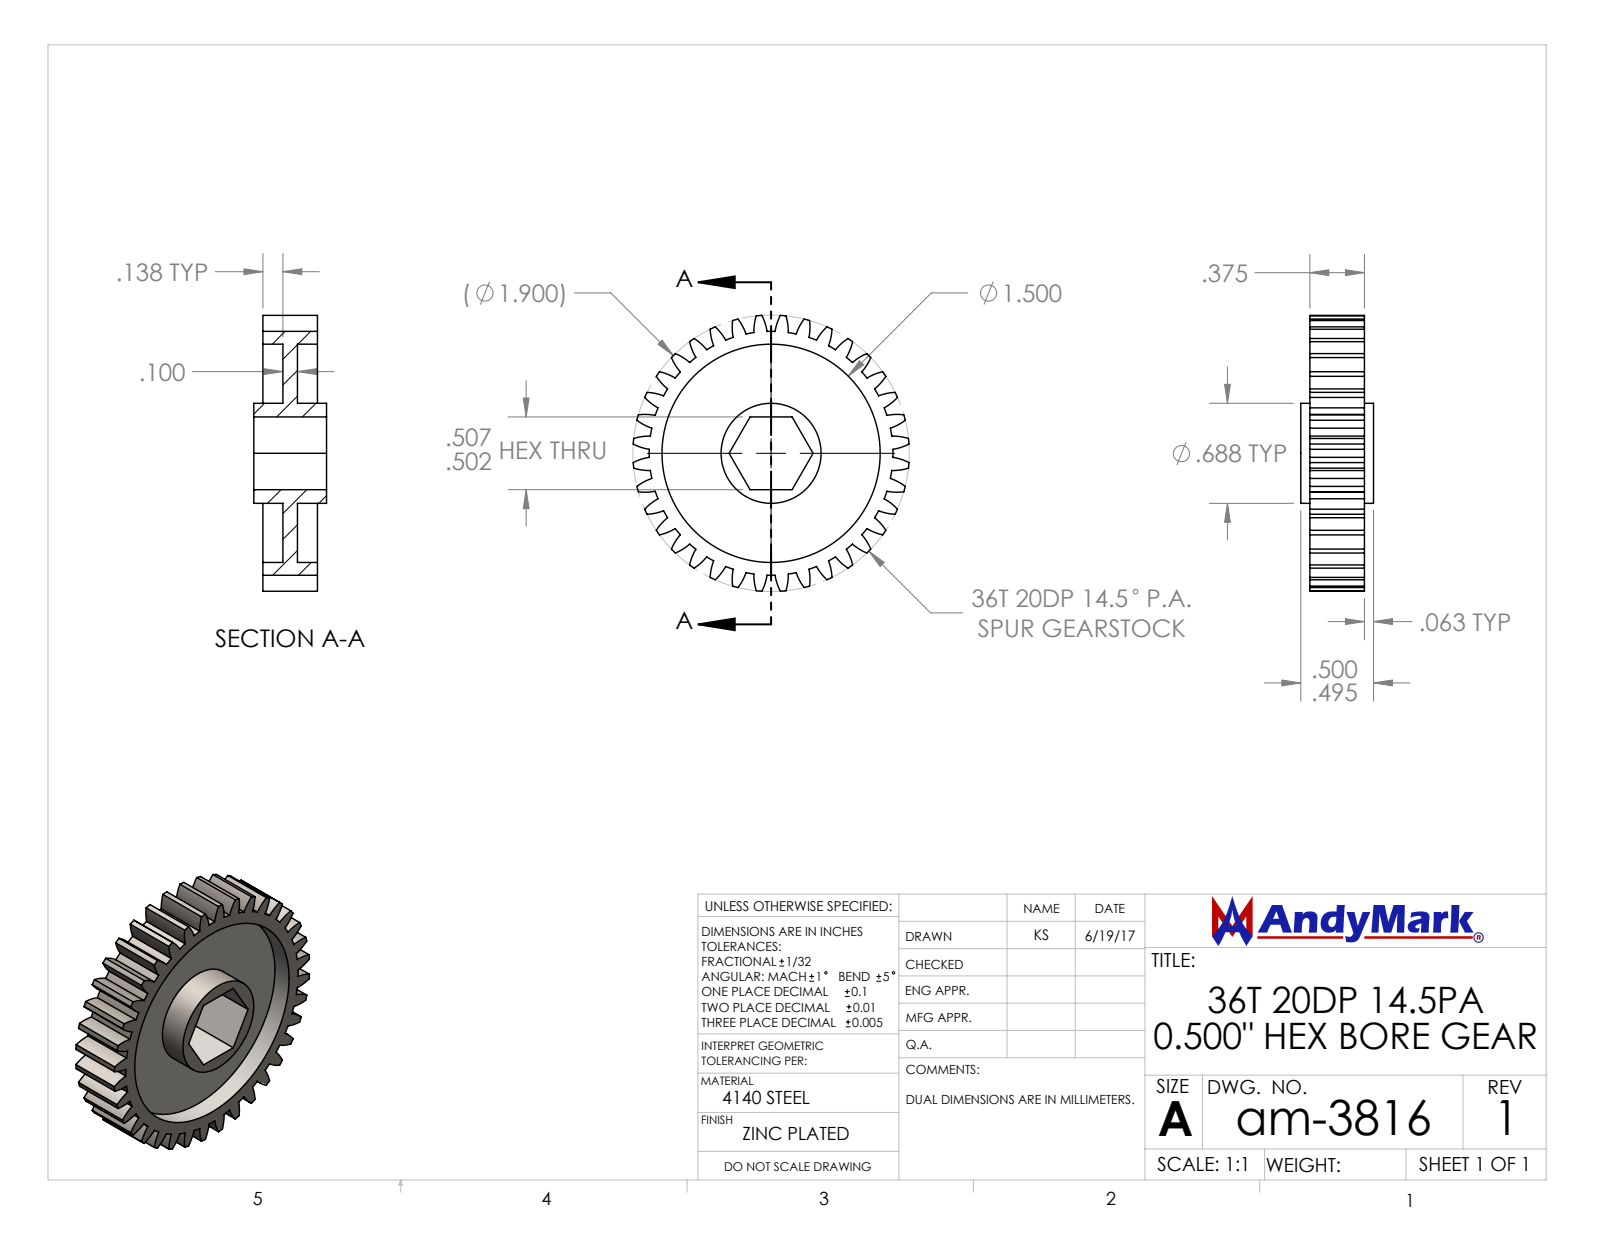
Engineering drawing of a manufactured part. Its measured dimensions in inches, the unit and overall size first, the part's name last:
Units: inches
Overall size (bounding box): 1.896 × 1.896 × 0.5
Round holes (diameter × count): ⌀1.5 ×1
Round bosses / shafts (diameter × count): ⌀0.75 ×1
Partial cylindrical surfaces — rounded edges, fillets, slot ends (radius × count): R0.36 ×72, R0.838 ×1, R0.95 ×1
Main face-to-face distances: 0.1, 0.137, 0.237, 0.375, 0.238, 0.138, 0.5, 0.2, 0.3, 0.437
Volume: 0.513 in³ · Surface area: 11.88 in²
Bodies: 1 solid, 245 faces (12 planar, 157 cylindrical, 76 other)
Part name (STEP PRODUCT): am-3816 36T 20DP 500hex 375 FW
STEP written by: SolidWorks 2021 (CONFIG_CONTROL_DESIGN)
